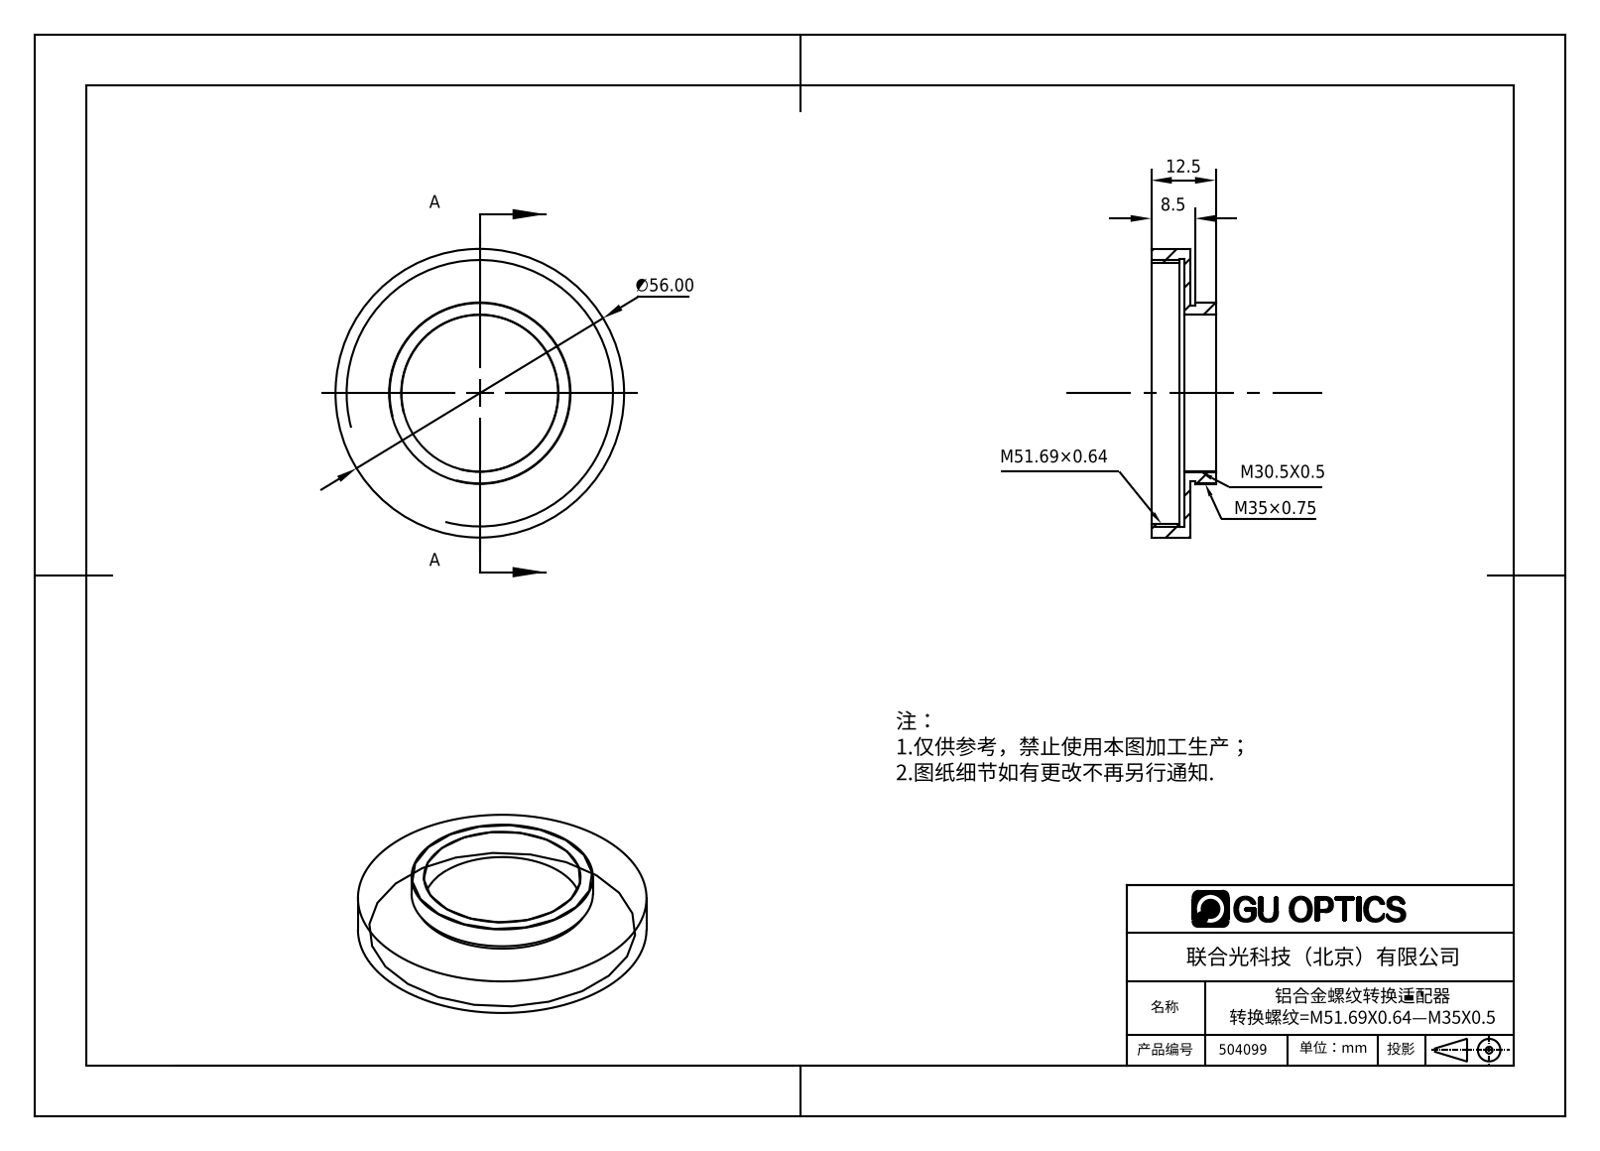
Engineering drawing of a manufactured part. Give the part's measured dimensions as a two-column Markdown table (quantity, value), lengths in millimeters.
| quantity | value |
| --- | --- |
| part name | 504098 |
| STEP written by | SolidWorks 2016 (AUTOMOTIVE_DESIGN) |
| units | millimeters |
| bodies | 1 solid, 18 faces (6 planar, 12 cylindrical, 0 other) |
| overall size | 56 × 56 × 12.5 |
| volume | 5 743 mm³ |
| surface area | 7 293 mm² |
| round holes (diameter × count) | 30.4 × 1, 50.6 × 1, 51.9 × 1 |
| round bosses / shafts (diameter × count) | 56 × 1, 35.2 × 1, 34 × 1 |
| main face-to-face distances | 1, 6.5, 7.5, 12.5, 6, 5, 2, 5.5, 7, 8.5 |
